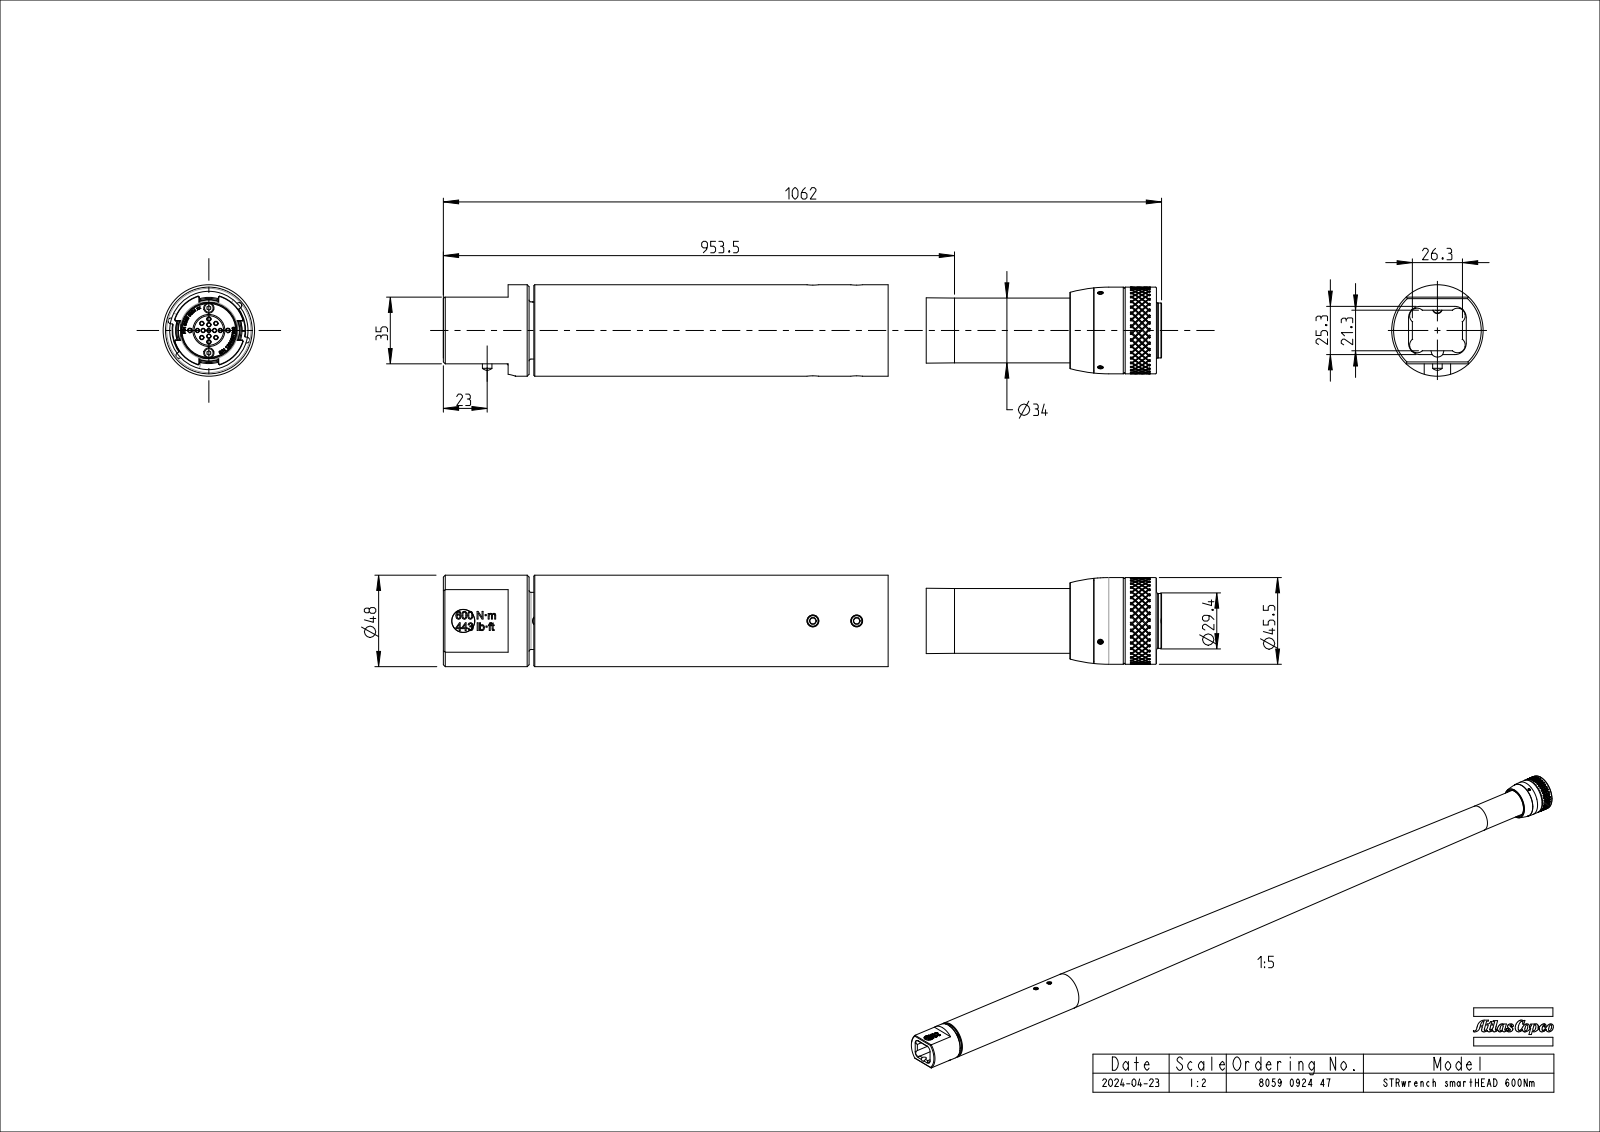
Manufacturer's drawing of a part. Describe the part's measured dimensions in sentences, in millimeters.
The part is named "8059092447". Its 3-D file was written by "CREO PARAMETRIC BY PTC INC, 2022414 (CONFIG_CONTROL_DESIGN)". It is 1 solid with 3102 faces: 548 planar, 454 cylindrical and 2100 other. Overall it measures 1062.2 by 48 by 48 millimeters. Its volume is 1 458 000 cubic millimeters and its surface area 166 275 square millimeters. Round holes: 12 of diameter 2.3, 5 of diameter 3, 4 of diameter 2.05, 3 of diameter 2.5, 3 of diameter 2.6, 2 of diameter 2.7, 2 of diameter 4, 2 of diameter 6.2, 1 of diameter 2.1, 1 of diameter 3.2, 1 of diameter 5, 1 of diameter 5.2. Round bosses or shafts: 13 of diameter 1.98, 4 of diameter 3, 4 of diameter 2.5, 3 of diameter 2, 2 of diameter 6.1, 2 of diameter 4.5, 1 of diameter 48, 1 of diameter 45.5. Partial cylindrical surfaces (rounded edges, fillets, slot ends): 5 of radius 4, 4 of radius 0.2, 4 of radius 0.4, 4 of radius 1.5, 4 of radius 5, 3 of radius 0.92, 2 of radius 1.72, 1 of radius 0.89. The main face-to-face distances are 35, 15.5, 4.5, 6.85, 11, 28.15, 49.5, 45, 34, 985.1. The hole center spacings are 3, 3.77, 4.36, 6.71, 7.65, 10.38, 6, 4.24.
